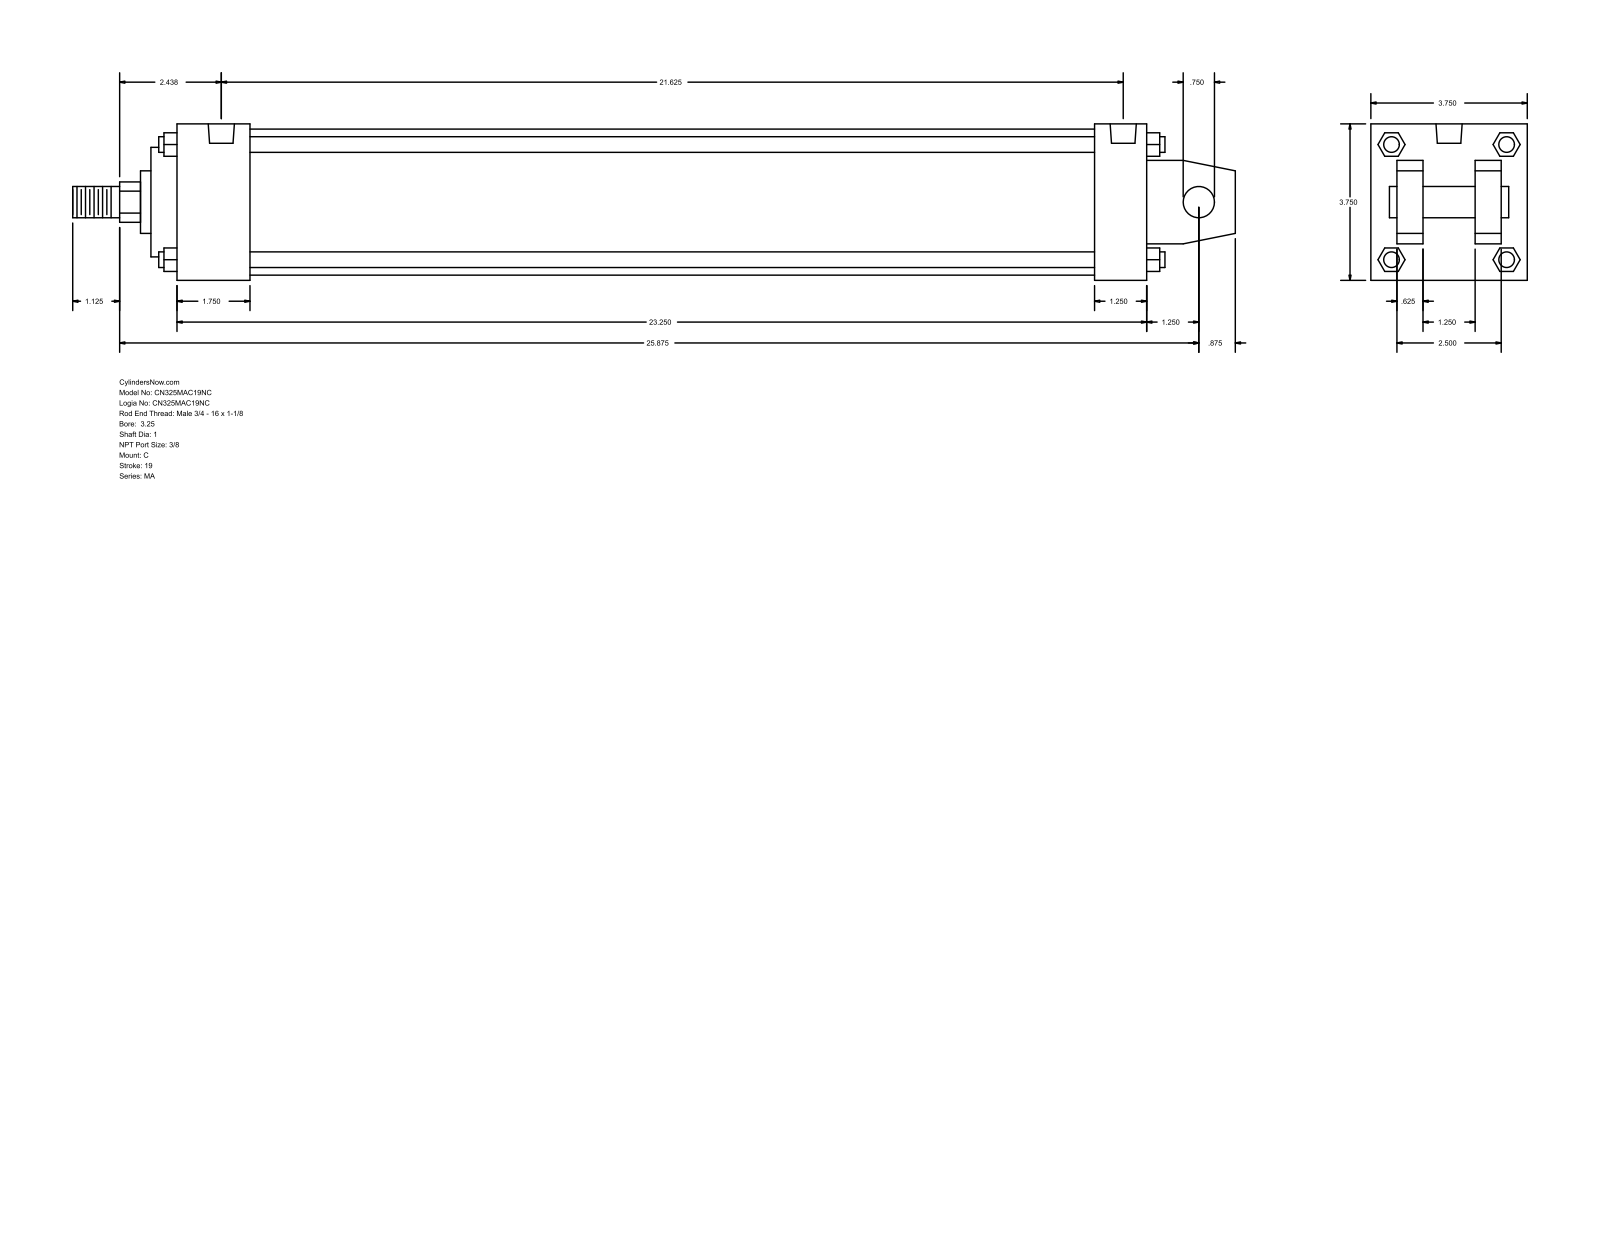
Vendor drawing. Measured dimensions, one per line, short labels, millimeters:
name: MA_C__0325_1
written by: GSSL Pune (CONFIG_CONTROL_DESIGN)
unit: mm
bodies: 0 solids, 141 faces (109 planar, 32 cylindrical, 0 other)
size: 708.02 × 95.25 × 95.25
holes: 4× ⌀11.11, 2× ⌀15.93
bosses: 4× ⌀9.53, 2× ⌀19.05, 1× ⌀88.9, 1× ⌀66.67, 1× ⌀38.1, 1× ⌀25.4
rounds: 1× R12.29
face distances: 95.24, 15.87, 63.5, 590.56, 31.74, 79.37, 47.63, 558.81, 31.75, 44.46
hole spacings: 539.75, 4.76, 4.77, 544.51, 544.52, 549.28
